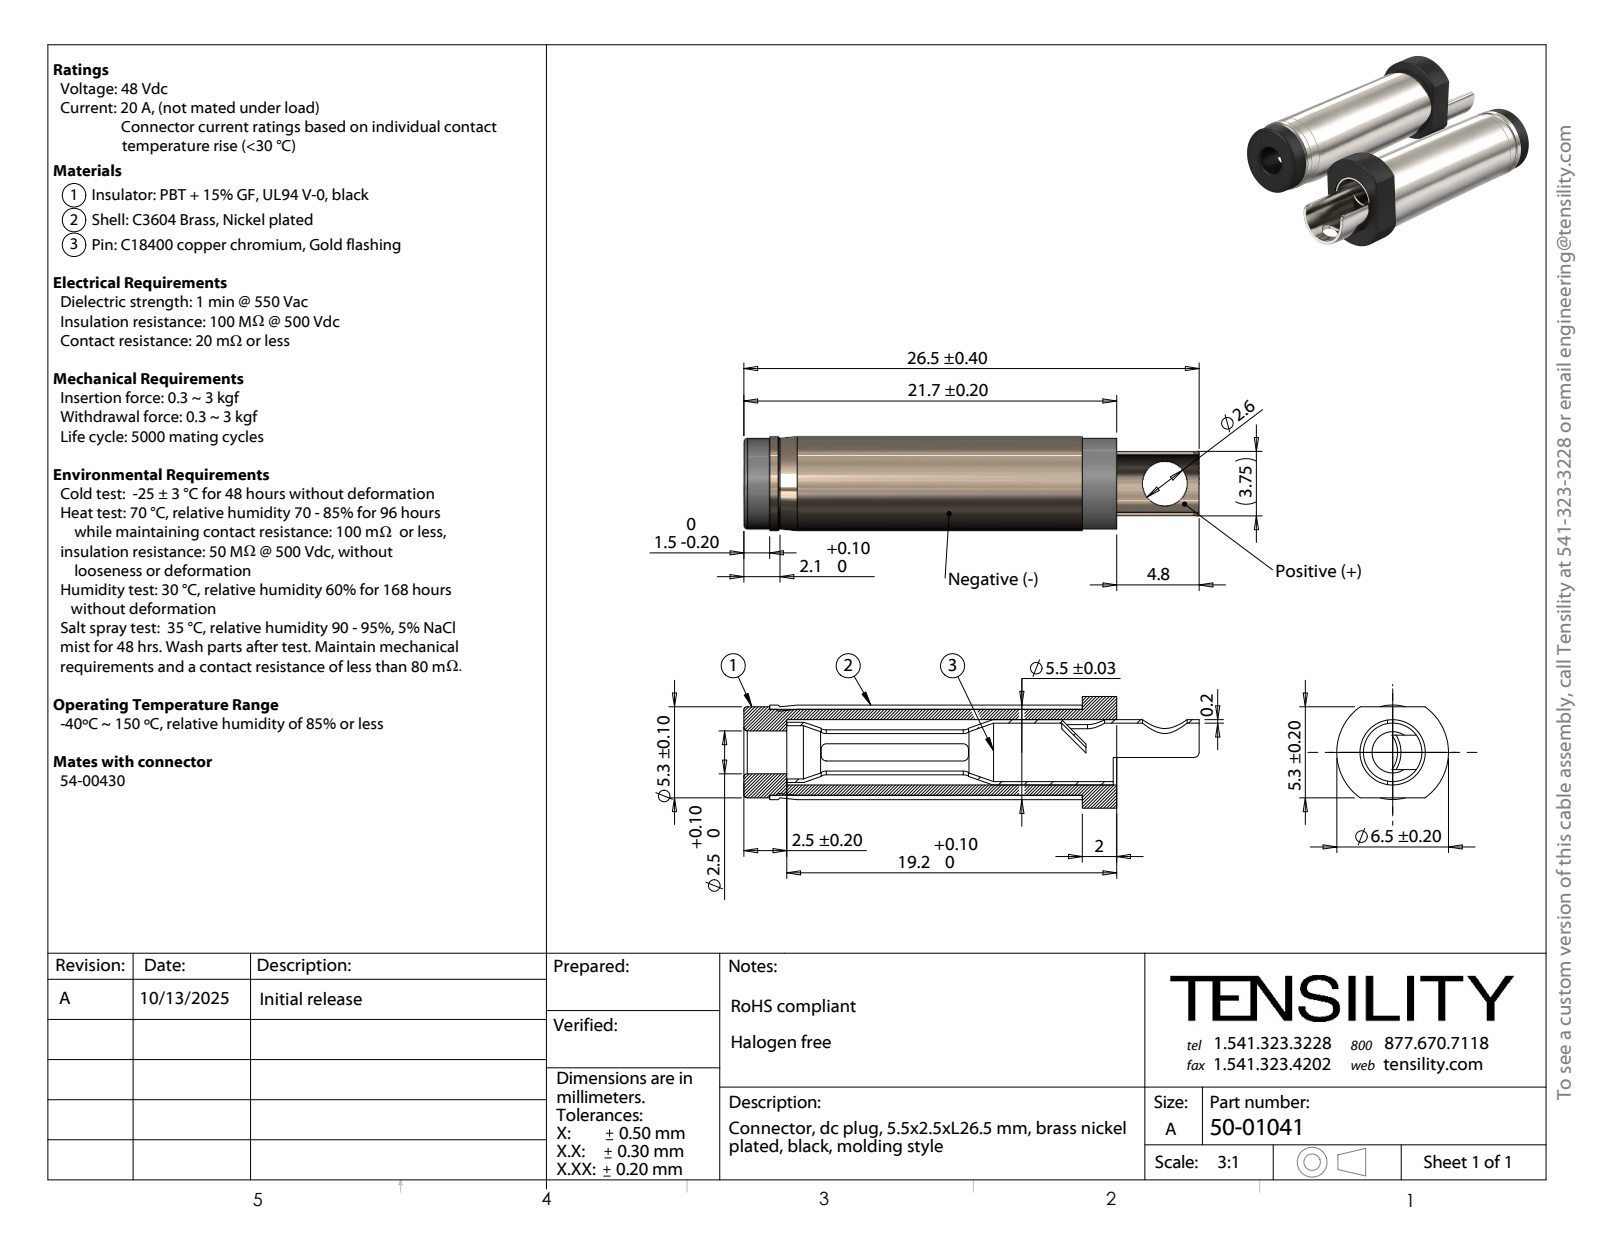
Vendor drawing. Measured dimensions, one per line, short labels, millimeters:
name: 50-01041-03_默认; 50-01041-01_默认; 50-01041; 50-01041-02_默认
written by: SolidWorks 2025 (CONFIG_CONTROL_DESIGN)
unit: mm
bodies: 3 solids, 110 faces (35 planar, 53 cylindrical, 22 other)
size: 26.6 × 6.7 × 5.5
volume: 336 mm³; area: 1 651 mm²
holes: 1× ⌀2.3, 1× ⌀2.4, 1× ⌀2.5, 1× ⌀3.1, 1× ⌀3.5, 1× ⌀3.8, 1× ⌀5
bosses: 1× ⌀5.5, 1× ⌀5.3, 1× ⌀3.9, 1× ⌀2.8
rounds: 9× R0.3, 1× R1, 1× R3.35
face distances: 2, 21.7, 19.7, 17.1, 19.1, 2.6, 1.5, 5.5, 2.25, 3.25
